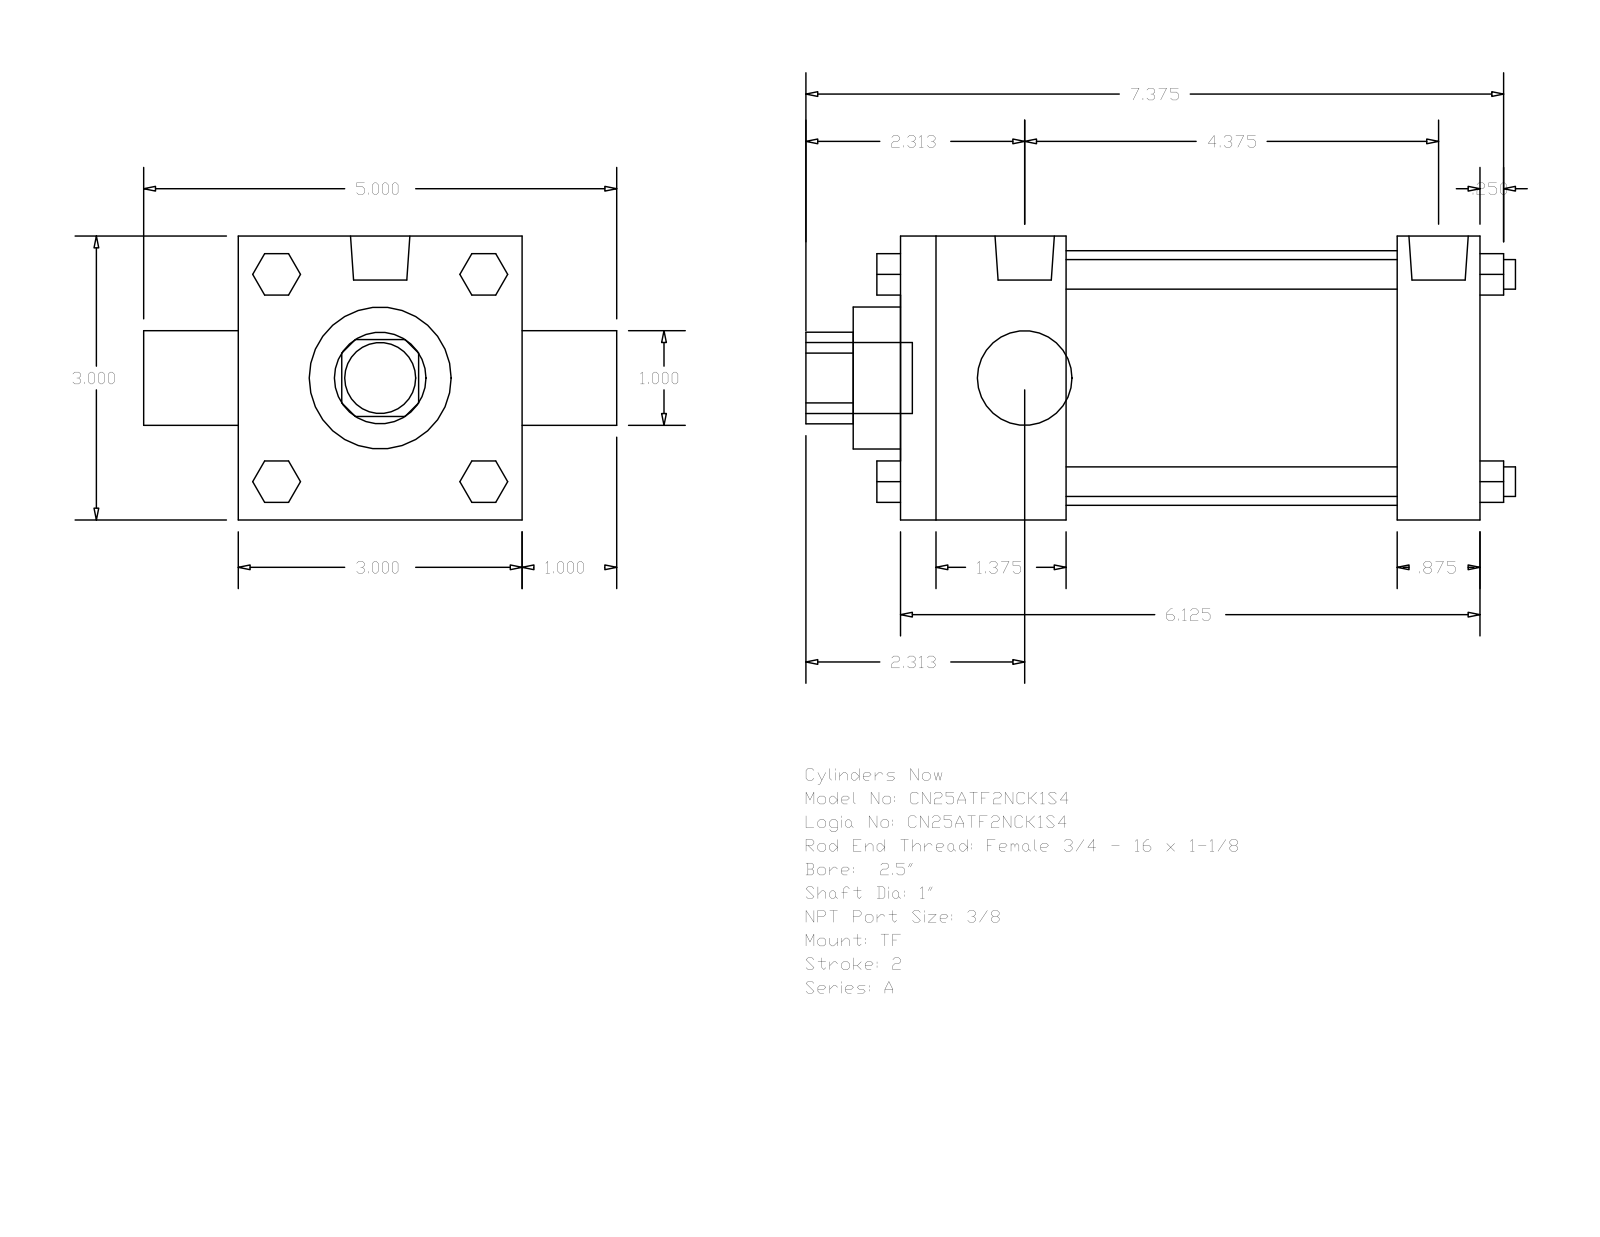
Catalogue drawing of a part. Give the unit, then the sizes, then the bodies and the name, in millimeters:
Units: millimetres
Overall size (bounding box): 190.5 × 127 × 76.2
Round holes (diameter × count): ⌀25.4 ×2, ⌀38.1 ×1, ⌀68.33 ×1
Round bosses / shafts (diameter × count): ⌀7.94 ×4, ⌀5.56 ×3, ⌀15.93 ×2, ⌀19.05 ×1
Partial cylindrical surfaces — rounded edges, fillets, slot ends (radius × count): R12.29 ×1
Main face-to-face distances: 76.2, 155.57, 44.45, 133.35, 88.9, 111.12, 22.22, 25.4, 101.6, 168.27
Bodies: 0 solids, 120 faces (92 planar, 28 cylindrical, 0 other)
Part name (STEP PRODUCT): A_TF__0250_1
STEP written by: GSSL Pune (CONFIG_CONTROL_DESIGN)
